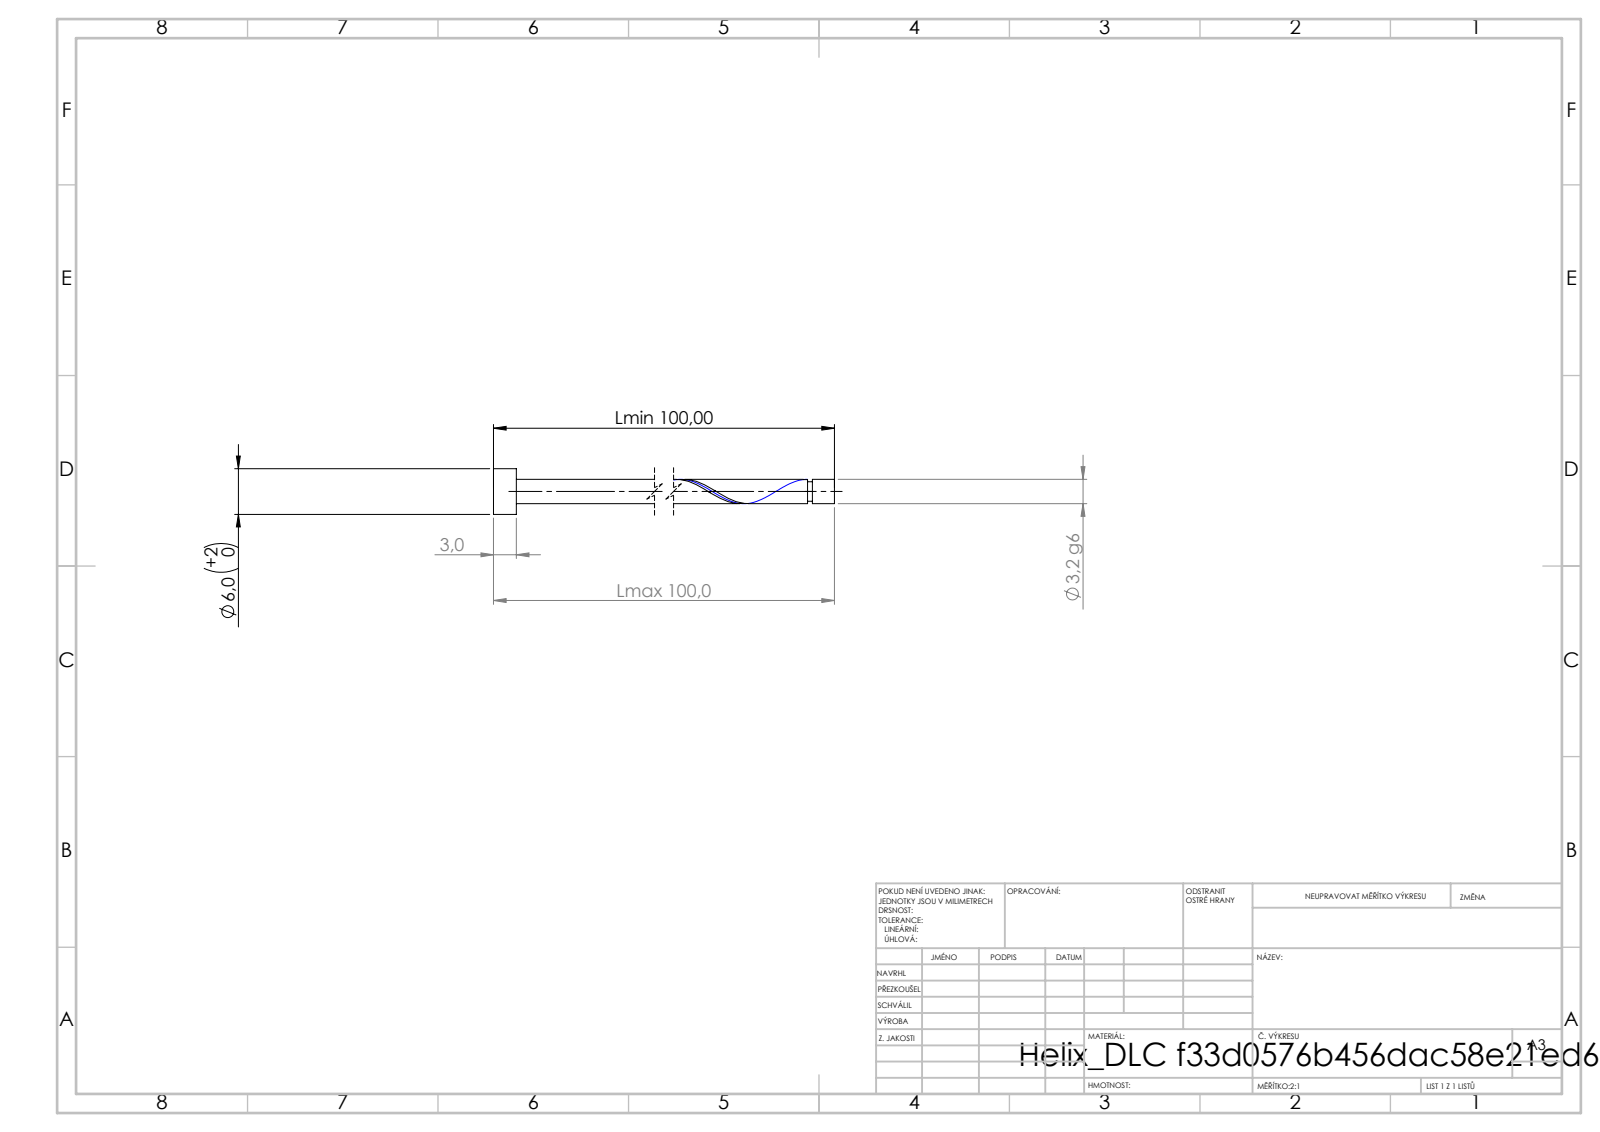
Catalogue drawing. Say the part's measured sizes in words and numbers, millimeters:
Its 3-D file was written by "SolidWorks 2019 (CONFIG_CONTROL_DESIGN)". It is 1 solid with 21 faces: 6 planar, 14 cylindrical and 1 other. Overall it measures 100 by 6 by 6 millimeters. Its volume is 855 cubic millimeters and its surface area 1 112 square millimeters. Round bosses or shafts: 1 of diameter 6, 1 of diameter 3.2, 1 of diameter 2.56. The main face-to-face distances are 3, 100, 97, 97.1, 94.1, 2.9, 96.46, 93.46, 0.64, 3.54.
